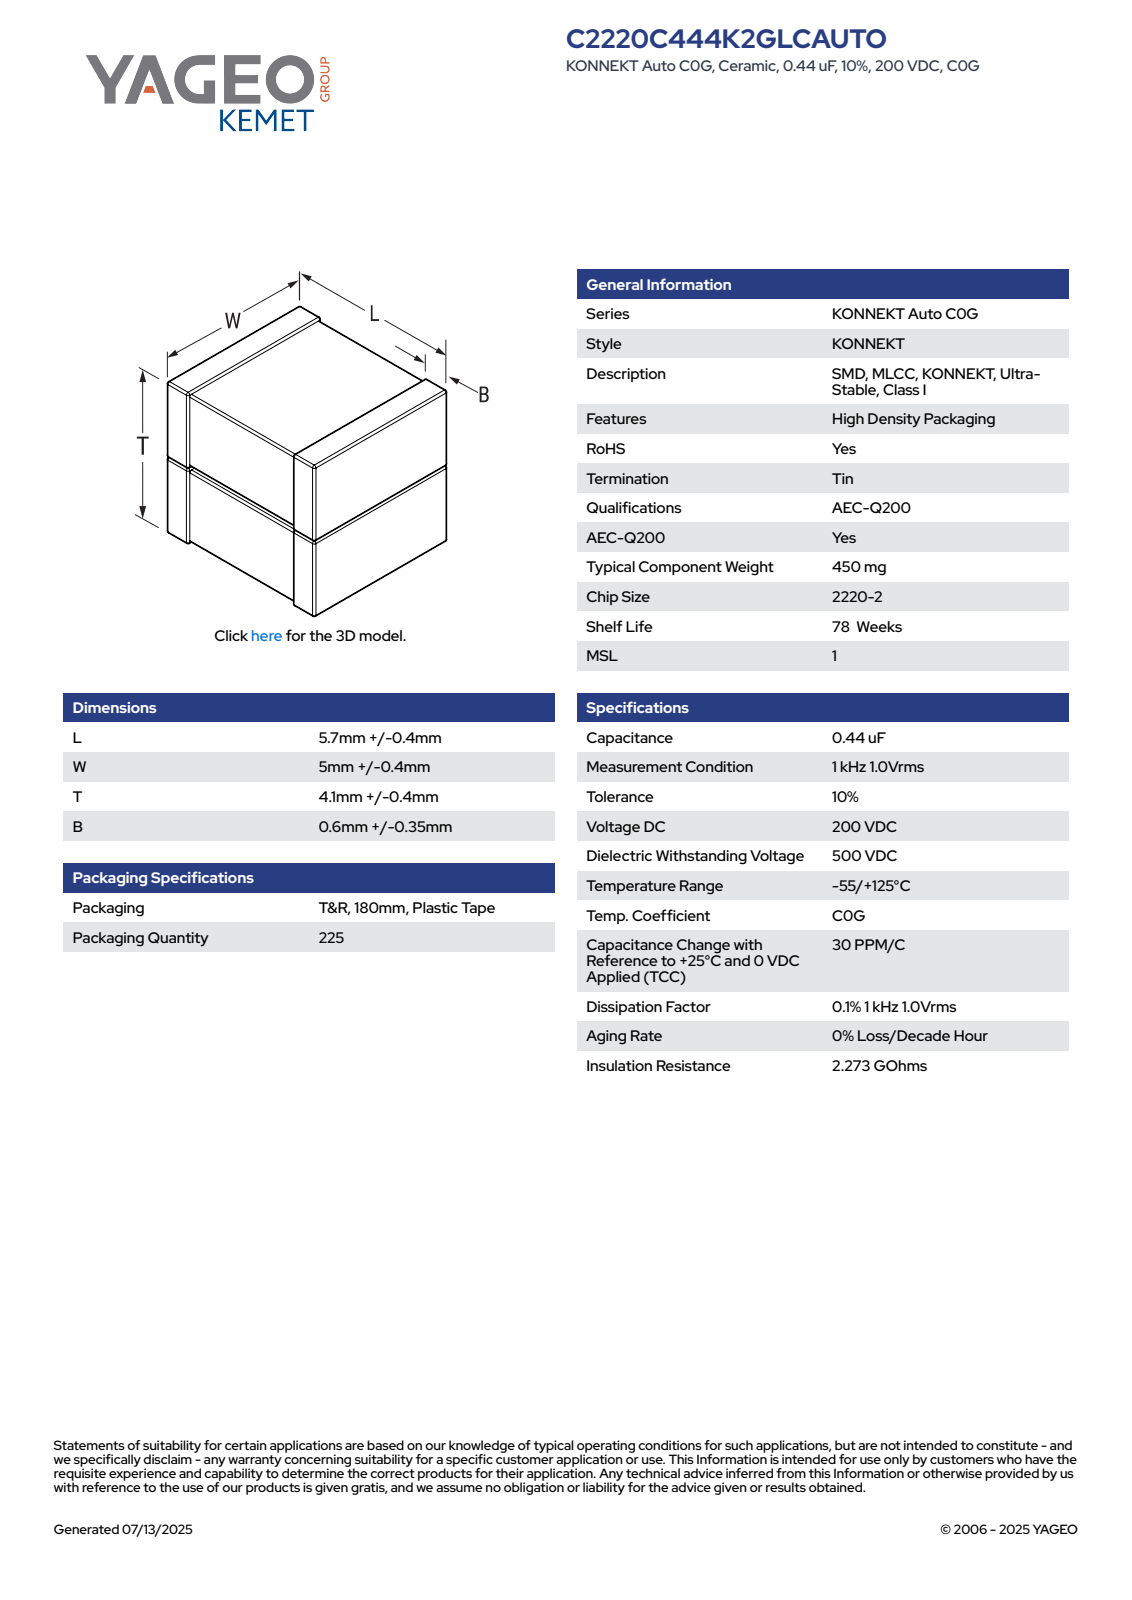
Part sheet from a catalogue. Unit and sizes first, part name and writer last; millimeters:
Units: millimetres
Overall size (bounding box): 6.1 × 5.4 × 4.5
Main face-to-face distances: 2.11, 2.25, 6.1, 4.36, 2.18, 2.32, 4.43, 5.26, 5.33, 4.5
Volume: 139 mm³ · Surface area: 215 mm²
Bodies: 4 solids, 189 faces (81 planar, 76 cylindrical, 32 other)
Part name (STEP PRODUCT): CCSS_K2T_2220-2_L6.1W5.4B0.95T4.5
STEP written by: SolidWorks 2020 (AUTOMOTIVE_DESIGN)
